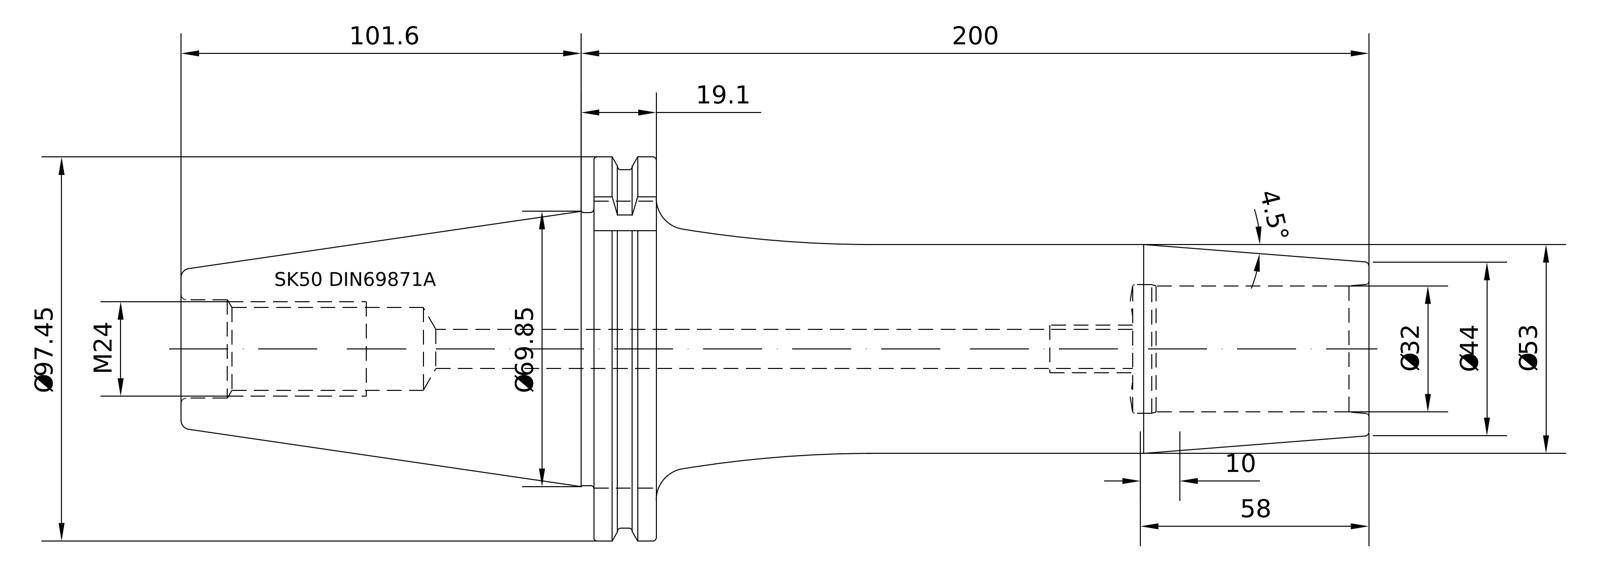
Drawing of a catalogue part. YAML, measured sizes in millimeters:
part_name: "50-446-32"
step_written_by: "PRO/ENGINEER BY PARAMETRIC TECHNOLOGY CORPORATION, 2010430 (CONFIG_CONTROL_DESIGN)"
units: millimeters
bodies: {solids: 1, faces: 96, planar: 22, cylindrical: 24, other: 50}
overall_size: [301.6, 97.47, 94]
volume: 689897
surface_area: 76381
round_holes:
  - {diameter: 20.75, count: 1}
  - {diameter: 25.01, count: 1}
  - {diameter: 25.7, count: 1}
  - {diameter: 32, count: 1}
round_bosses_or_shafts:
  - {diameter: 91, count: 1}
  - {diameter: 69.15, count: 1}
  - {diameter: 53, count: 1}
  - {diameter: 24.01, count: 1}
partial_cylinders:
  - {radius: 1.75, count: 1}
  - {radius: 48.74, count: 1}
face_to_face_distances: [15.85, 138.8, 122.95, 196.8, 180.95, 58, 72.8, 104.8, 120.65, 243.6]
